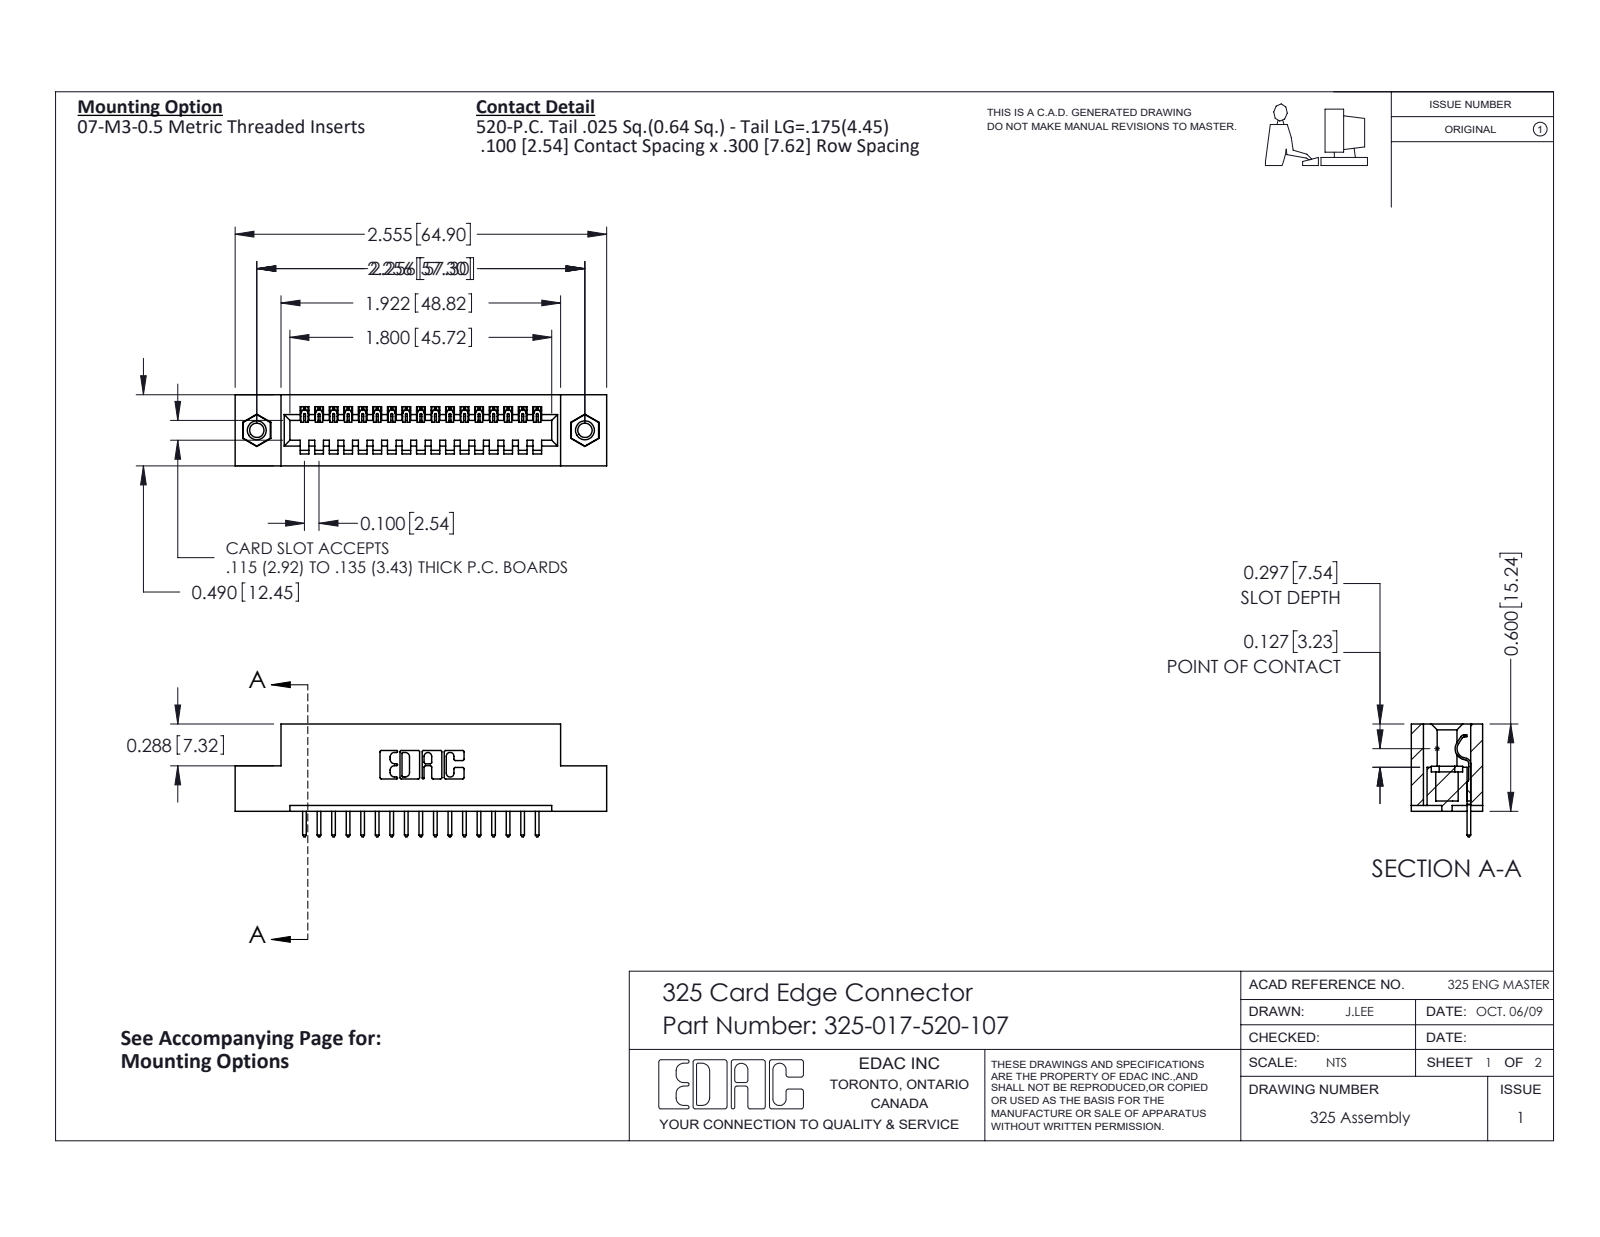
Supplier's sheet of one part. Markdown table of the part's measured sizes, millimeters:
| quantity | value |
| --- | --- |
| part name | 325 Part_TI; 325-017-520-107; 345-250-001_345-250-005-103; 325-292-001_325-293-120 |
| STEP written by | SolidWorks 2016 (CONFIG_CONTROL_DESIGN) |
| units | millimeters |
| bodies | 20 solids, 1160 faces (816 planar, 328 cylindrical, 16 other) |
| overall size | 64.9 × 19.7 × 12.4 |
| volume | 7 980 mm³ |
| surface area | 8 148 mm² |
| round holes (diameter × count) | 2.5 × 2, 3.2 × 2, 4.1 × 2 |
| round bosses / shafts (diameter × count) | 3.9 × 2 |
| partial cylindrical surfaces (radius × count) | 0.2 × 34, 0.3 × 34, 0.3 × 22, 0.2 × 6, 0.8 × 6, 0.7 × 3, 0.4 × 1, 0.6 × 1 |
| main face-to-face distances | 2.1, 10.3, 7.6, 12.4, 15.2, 2.7, 9.7, 0.6, 1, 5.1 |
| hole center spacings | 57.3 |
